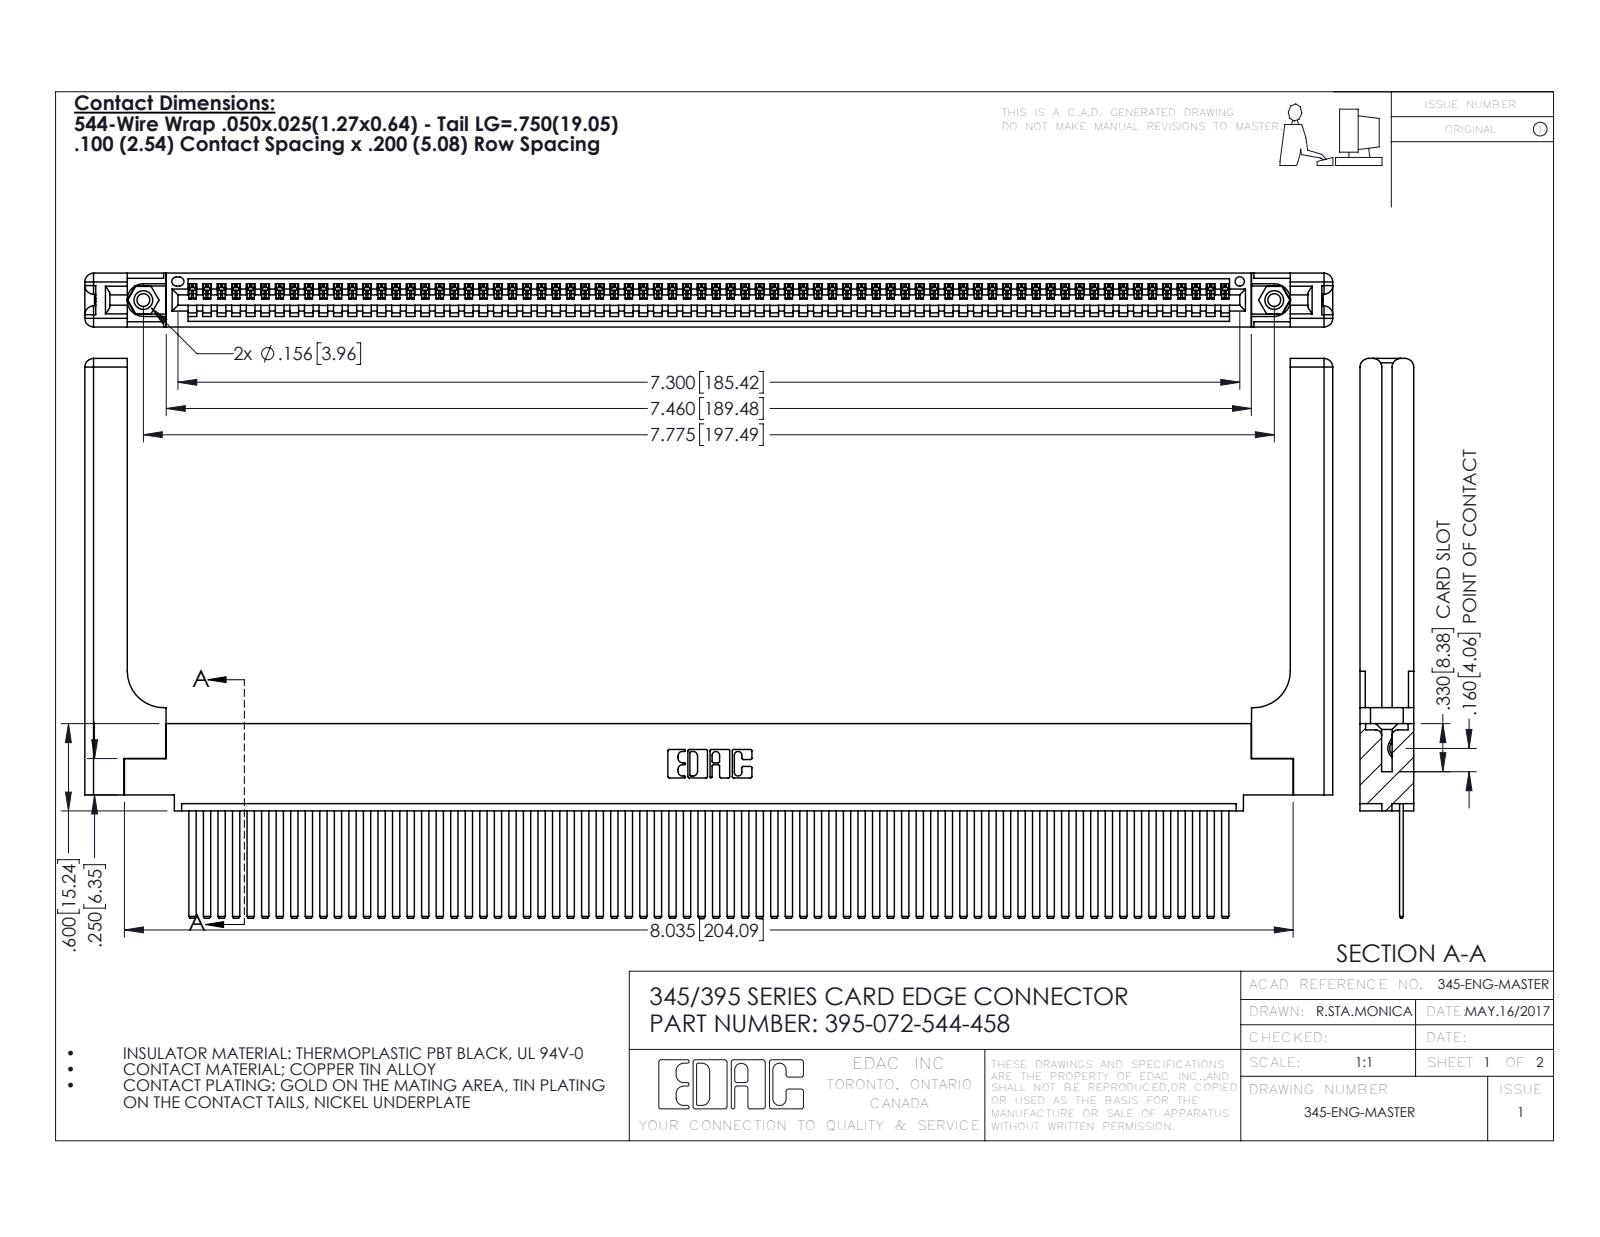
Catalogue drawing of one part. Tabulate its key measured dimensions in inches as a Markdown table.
| quantity | value |
| --- | --- |
| part name | 345-220-058_345-220-058; 345-250-001_345-250-001-102; 345-292-001_345-293-144; 345 Part_0.110 Offset - 0.156 Dia-TH (+1 more) |
| STEP written by | SolidWorks 2016 (CONFIG_CONTROL_DESIGN) |
| units | inches |
| bodies | 77 solids, 4130 faces (2824 planar, 1246 cylindrical, 60 other) |
| overall size | 8.579 × 3.847 × 0.37 |
| volume | 1.843 in³ |
| surface area | 57.57 in² |
| round holes (diameter × count) | 0.089 × 2, 0.125 × 2, 0.156 × 2, 0.064 × 1 |
| round bosses / shafts (diameter × count) | 0.155 × 2 |
| partial cylindrical surfaces (radius × count) | 0.006 × 144, 0.01 × 22, 0.06 × 16, 0.007 × 6, 0.031 × 6, 0.026 × 3, 0.03 × 2, 0.031 × 2 |
| main face-to-face distances | 0.072, 0.298, 0.098, 0.272, 0.025, 0.37, 0.2, 0.225, 0.148, 0.15 |
| hole center spacings | 0.27, 7.539, 7.775 |
